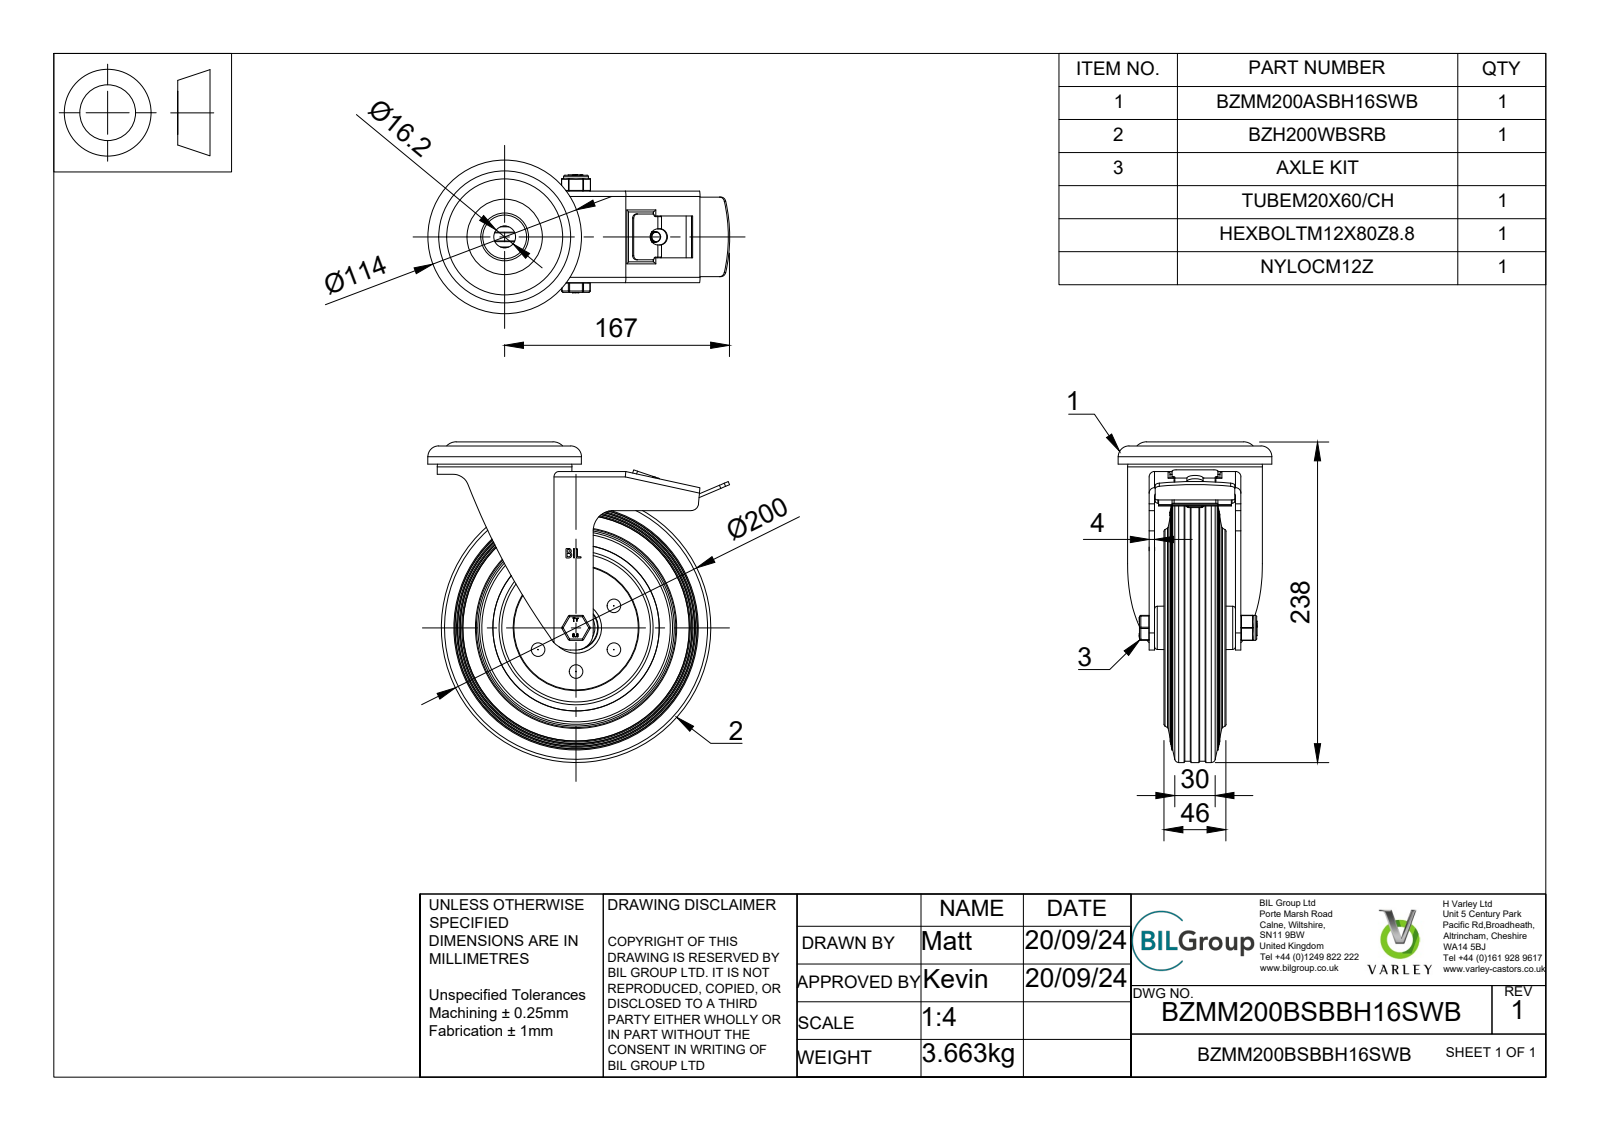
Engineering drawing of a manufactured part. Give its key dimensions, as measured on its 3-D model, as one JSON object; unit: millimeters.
{"part_name": "BZMM200BSBBH16SWB v3; BZMM200ASBH16SWB v1; ZINC PLATED, PRESSED STEEL HEAD; ZINC PLATED, PRESSED STEEL FORKS (+8 more)", "step_written_by": "Autodesk Translation Framework v13.20.0.188 (AUTOMOTIVE_DESIGN)", "units": "millimeters", "bodies": {"solids": 28, "faces": 827, "planar": 361, "cylindrical": 251, "other": 215}, "overall_size": [238, 224, 114], "volume_mm3": 1173000, "surface_area_mm2": 308637, "round_holes": [[5, 6], [8, 1], [12, 1], [12.2, 1], [12.5, 1], [14, 1], [16.2, 1], [20.2, 1], [21, 1], [30, 1], [41, 1], [52, 1]], "round_bosses_or_shafts": [[5, 10], [200, 1], [198, 1], [114, 1], [100, 1], [74, 1], [47, 1], [32.5, 1]], "partial_cylinders_radius": [[1, 37], [0.5, 23], [2, 12], [4, 7], [1.5, 6], [3, 2], [6, 2], [0.26, 1]], "face_to_face_distances": [4, 33, 31, 29, 35, 64, 2, 2.5, 1, 60], "hole_center_spacings": [32.5, 56.29, 56.3, 65.01, 65]}
